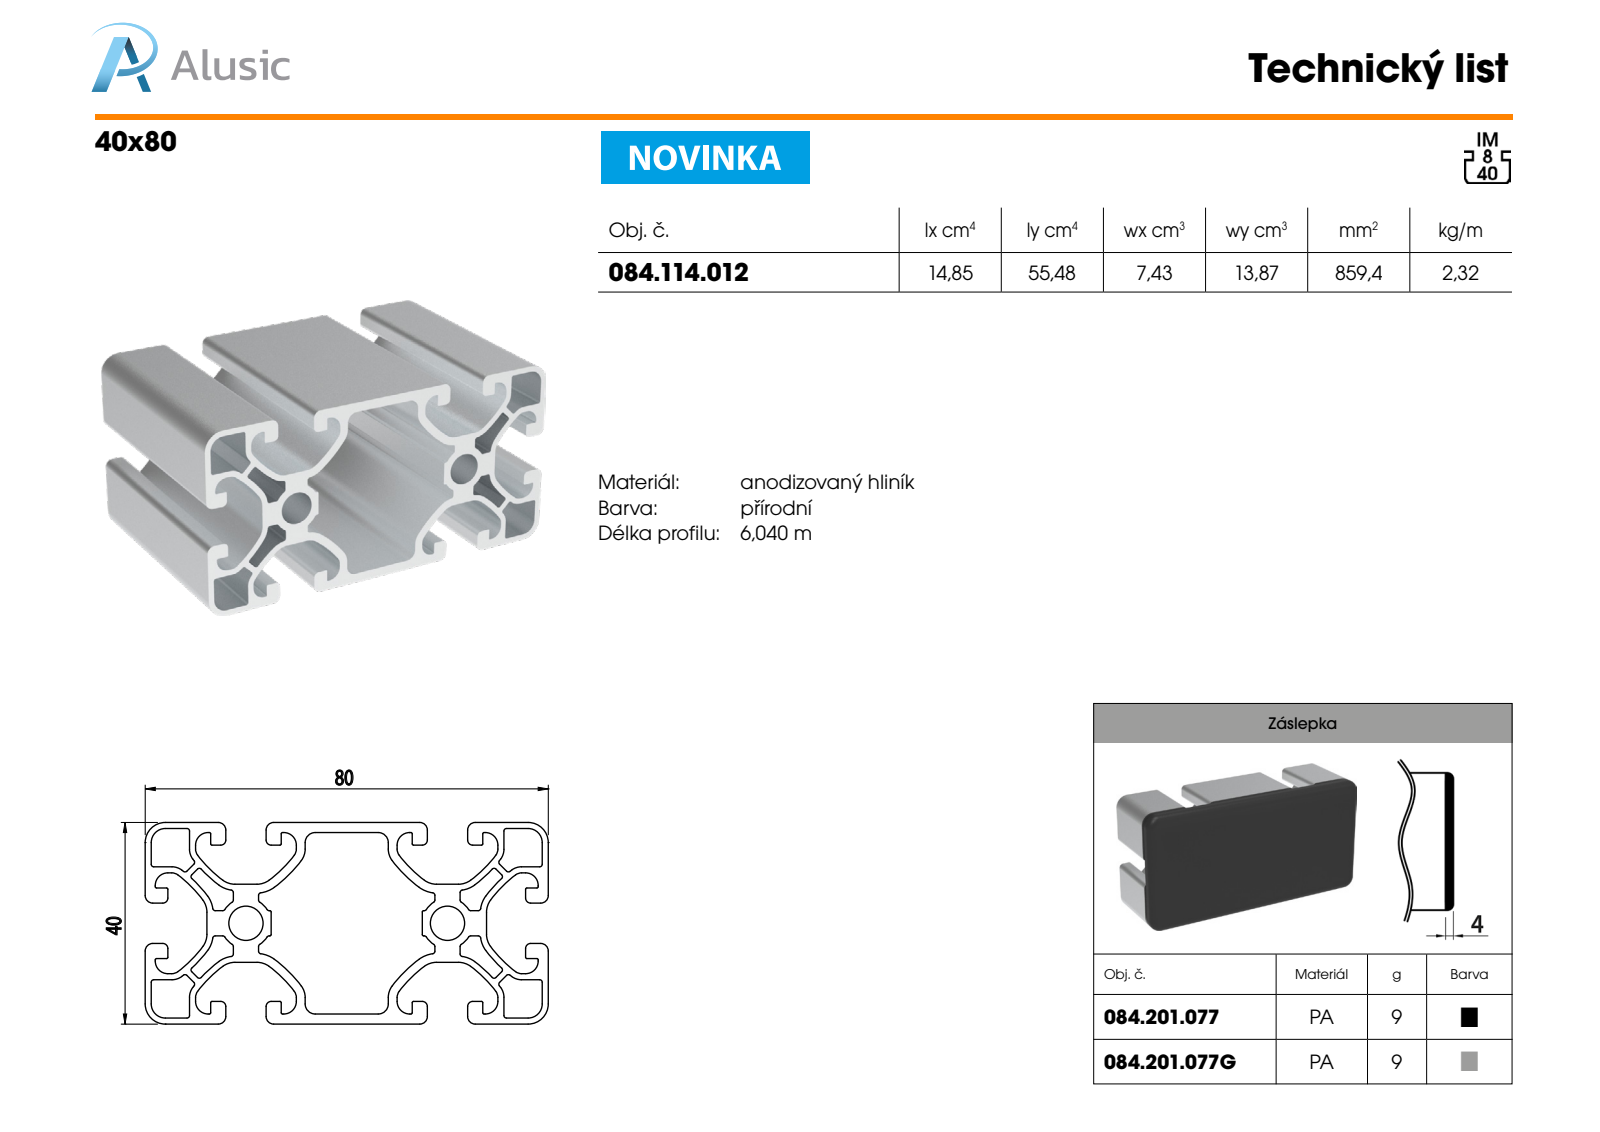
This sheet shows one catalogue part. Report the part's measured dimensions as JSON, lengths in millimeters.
{"part_name": "084.201.077", "step_written_by": "SolidWorks 2016 (CONFIG_CONTROL_DESIGN)", "units": "millimeters", "bodies": {"solids": 1, "faces": 99, "planar": 31, "cylindrical": 46, "other": 22}, "overall_size": [80, 40, 10.5], "volume_mm3": 8848, "surface_area_mm2": 7996, "round_holes": [[10, 2]], "round_bosses_or_shafts": [[12, 2]], "partial_cylinders_radius": [[0.3, 6], [2, 4], [2.5, 4], [4, 4], [3.55, 2]], "face_to_face_distances": [2.5, 4, 1.5, 19.4, 16.9, 20.6, 18.1, 37.5, 40, 1.2], "hole_center_spacings": [40]}
